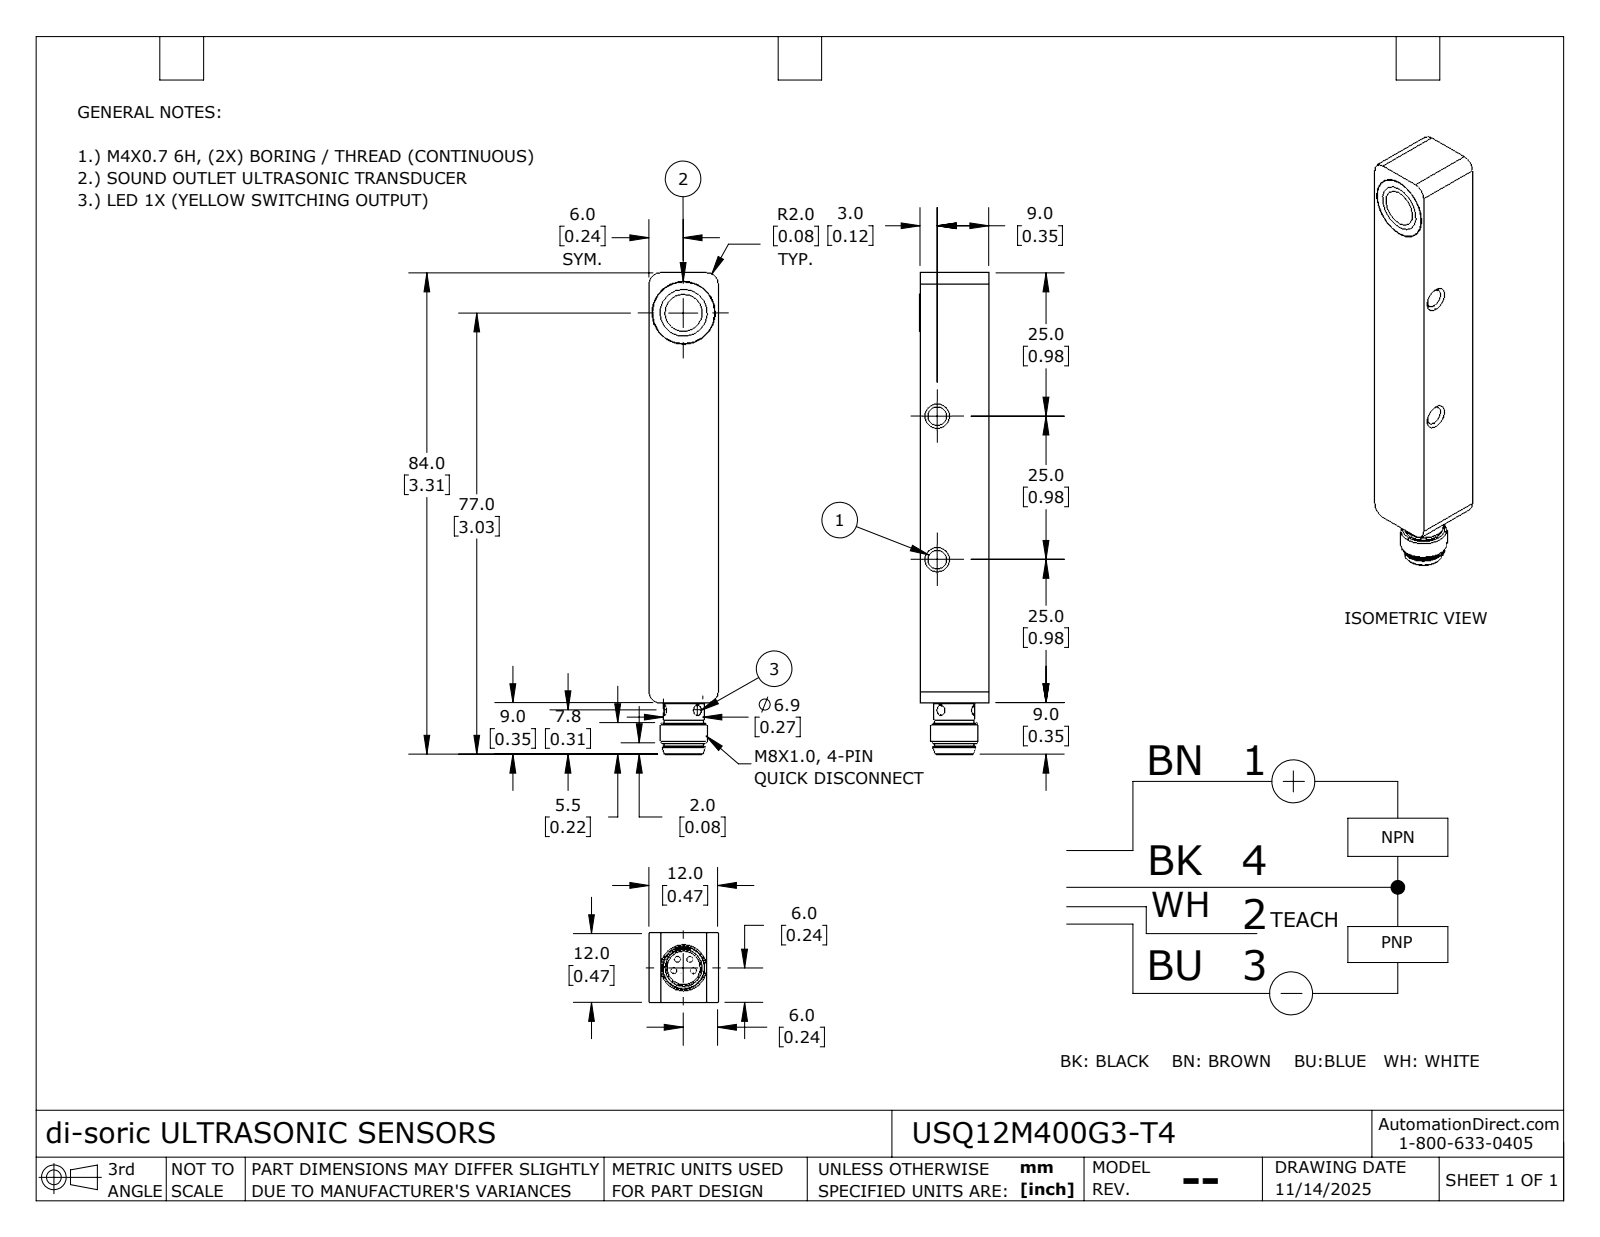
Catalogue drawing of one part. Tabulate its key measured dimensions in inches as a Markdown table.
| quantity | value |
| --- | --- |
| part name | USQ12M200G3-T4 |
| STEP written by | SolidWorks 2024 (AUTOMOTIVE_DESIGN) |
| units | inches |
| bodies | 1 solid, 104 faces (36 planar, 53 cylindrical, 15 other) |
| overall size | 3.307 × 0.474 × 0.473 |
| volume | 0.655 in³ |
| surface area | 7.485 in² |
| round holes (diameter × count) | 0.075 × 3, 0.128 × 2, 0.228 × 2, 0.079 × 1, 0.346 × 1, 0.406 × 1, 0.433 × 1 |
| round bosses / shafts (diameter × count) | 0.039 × 4, 0.425 × 1, 0.402 × 1, 0.323 × 1, 0.315 × 1, 0.283 × 1, 0.272 × 1, 0.26 × 1 |
| partial cylindrical surfaces (radius × count) | 0.079 × 4, 0.037 × 1 |
| main face-to-face distances | 0.472, 2.953, 0.473, 0.079, 0.078, 0.394, 0.04, 0.02, 0.039, 0.019 |
| hole center spacings | 0.984 |
